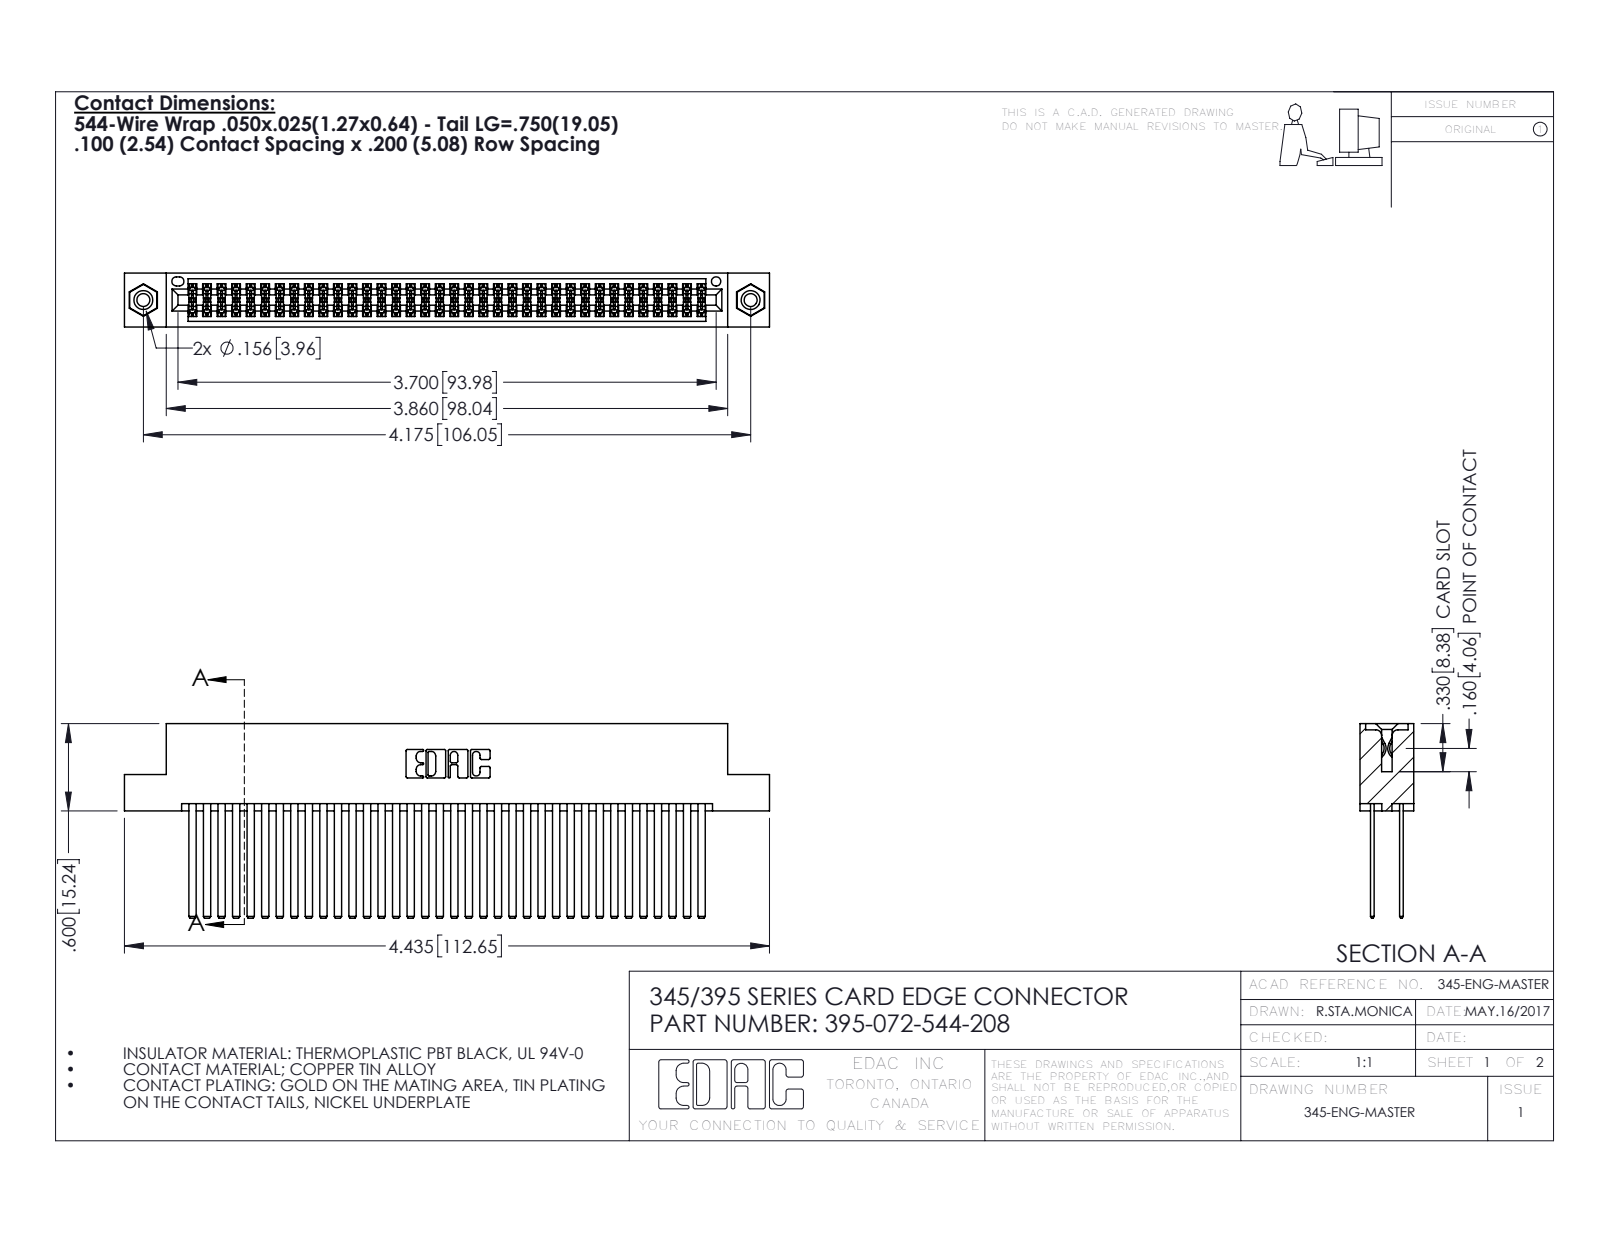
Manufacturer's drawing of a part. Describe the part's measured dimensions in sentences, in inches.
The part is named "345 Part_Flush Mounting Lugs - 0.156 Dia-TI; 345-250-001_345-250-003-102; 395-072-544-208; 345-292-001_345-293-144". Its 3-D file was written by "SolidWorks 2016 (CONFIG_CONTROL_DESIGN)". It is 75 solids with 3354 faces: 2200 planar, 1138 cylindrical and 16 other. Overall it measures 4.435 by 1.337 by 0.37 inches. Its volume is 0.726 cubic inches and its surface area 31.67 square inches. Round holes: 2 of diameter 0.089, 2 of diameter 0.125, 2 of diameter 0.156, 1 of diameter 0.064. Round bosses or shafts: 2 of diameter 0.155. Partial cylindrical surfaces (rounded edges, fillets, slot ends): 108 of radius 0.006, 22 of radius 0.01, 6 of radius 0.007, 6 of radius 0.031, 3 of radius 0.026, 2 of radius 0.014, 2 of radius 0.019, 2 of radius 0.022. The main face-to-face distances are 0.2, 0.025, 0.072, 0.098, 0.272, 0.298, 0.225, 0.175, 0.37, 0.05. The hole center spacings are 0.27, 3.939, 4.175.
